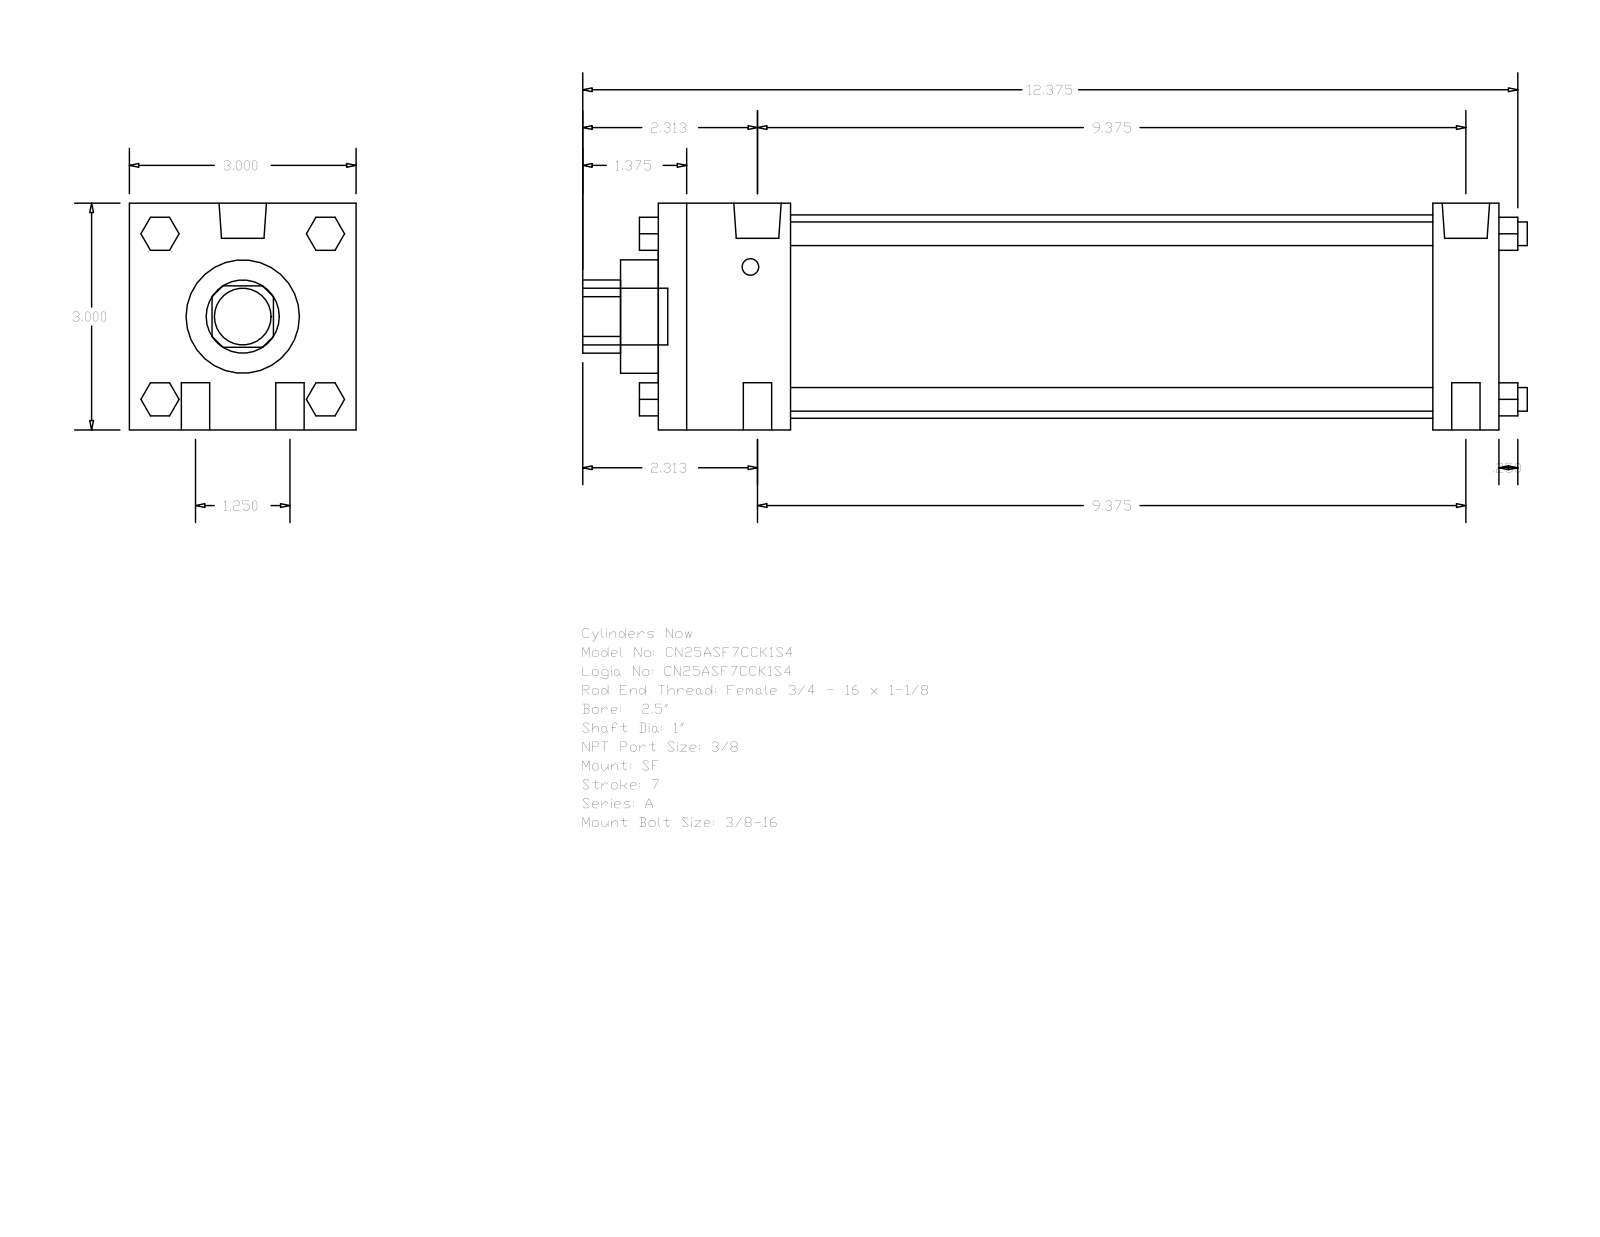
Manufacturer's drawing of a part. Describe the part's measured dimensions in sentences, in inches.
The part is named "A_SF__0250_1". Its 3-D file was written by "GSSL Pune (CONFIG_CONTROL_DESIGN)". It is 0 solids with 124 faces: 94 planar, 30 cylindrical and 0 other. Overall it measures 12.5 by 3 by 3 inches. Round holes: 1 of diameter 1, 1 of diameter 1.5, 1 of diameter 2.69. Round bosses or shafts: 4 of diameter 0.375, 4 of diameter 0.313, 2 of diameter 0.627, 2 of diameter 0.219, 1 of diameter 0.75. Partial cylindrical surfaces (rounded edges, fillets, slot ends): 1 of radius 0.484. The main face-to-face distances are 3, 11.125, 10.25, 0.875, 1.75, 8.5, 9.375, 0.5, 0.437, 2.25.
